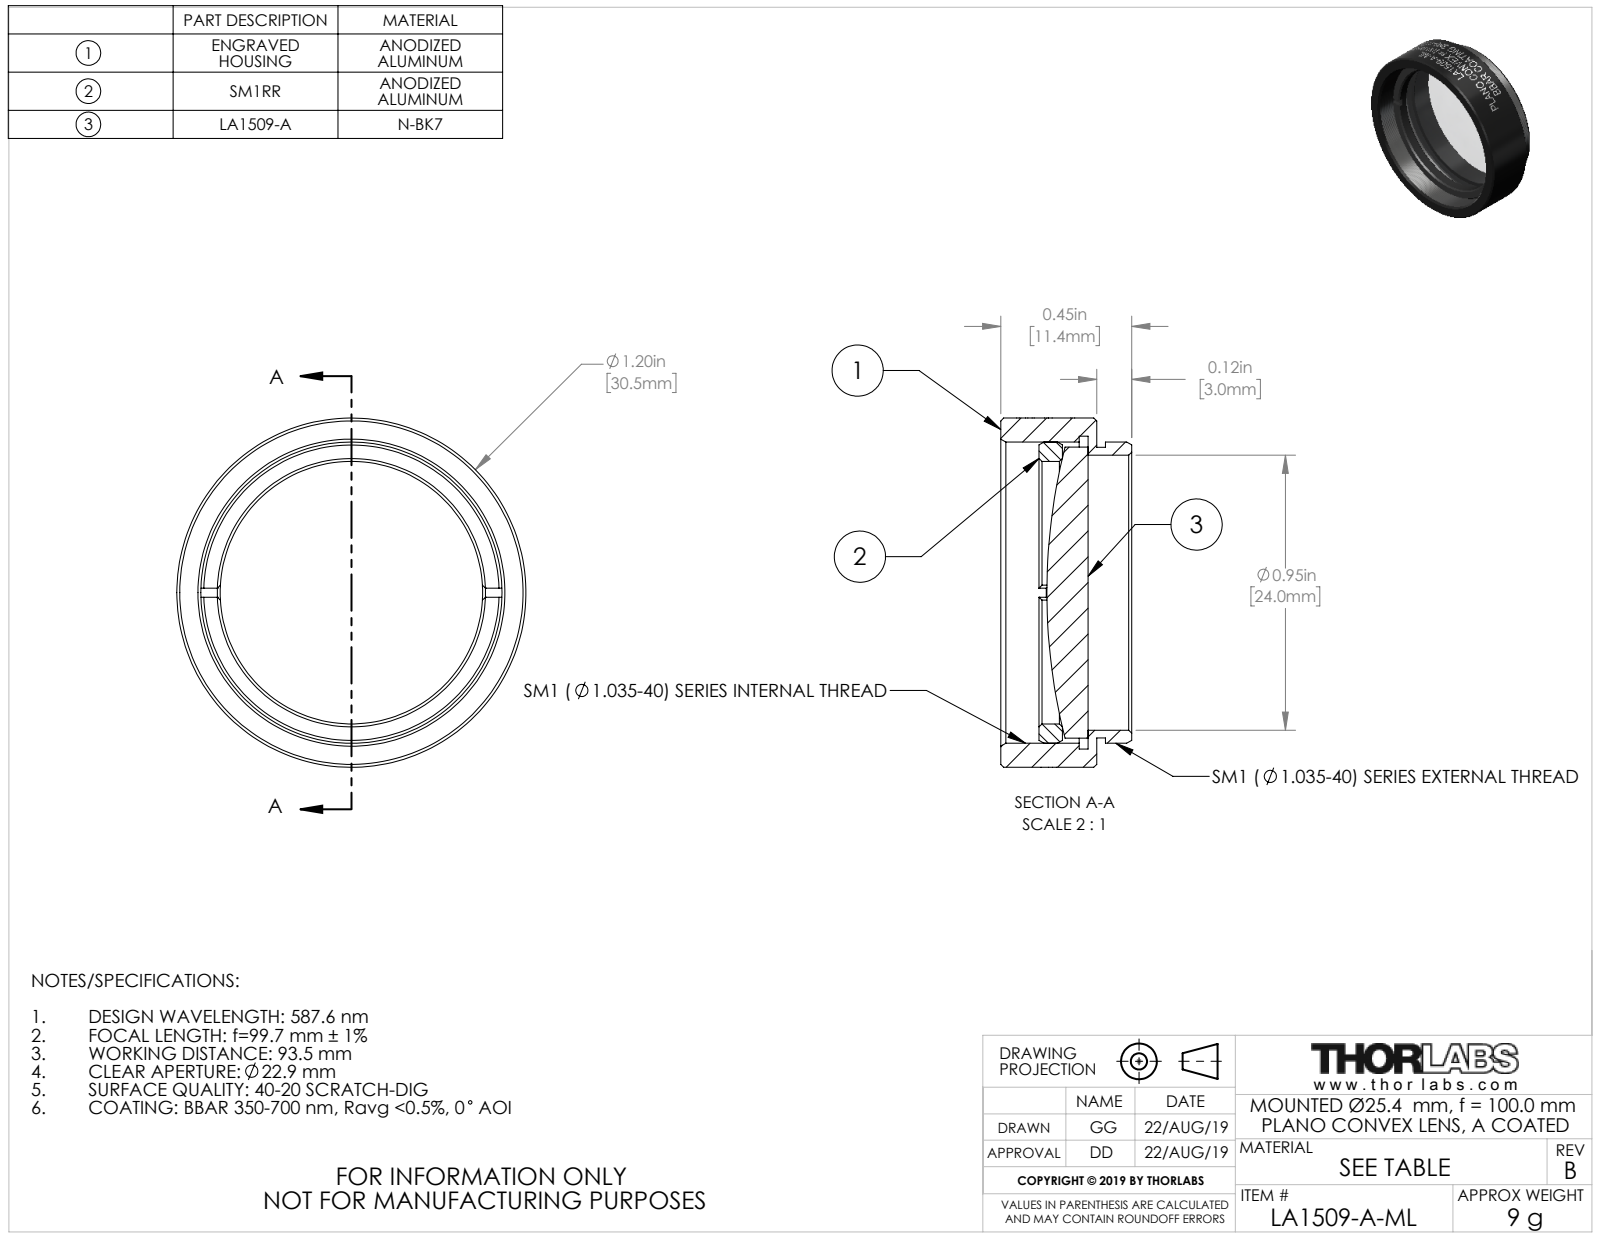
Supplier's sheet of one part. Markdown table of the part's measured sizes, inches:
| quantity | value |
| --- | --- |
| part name | 24411-E0W |
| STEP written by | SolidWorks 2018 (CONFIG_CONTROL_DESIGN) |
| units | inches |
| bodies | 3 solids, 153 faces (20 planar, 109 cylindrical, 24 other) |
| overall size | 1.2 × 1.2 × 0.45 |
| volume | 0.214 in³ |
| surface area | 6.696 in² |
| round holes (diameter × count) | 0.902 × 1, 0.945 × 1, 1.075 × 1 |
| round bosses / shafts (diameter × count) | 1.2 × 1, 1.035 × 1, 1 × 1, 0.999 × 1 |
| main face-to-face distances | 0.03, 0.33, 0.3, 0.118, 0.088, 0.212, 0.198, 0.168, 0.08, 0.132 |
